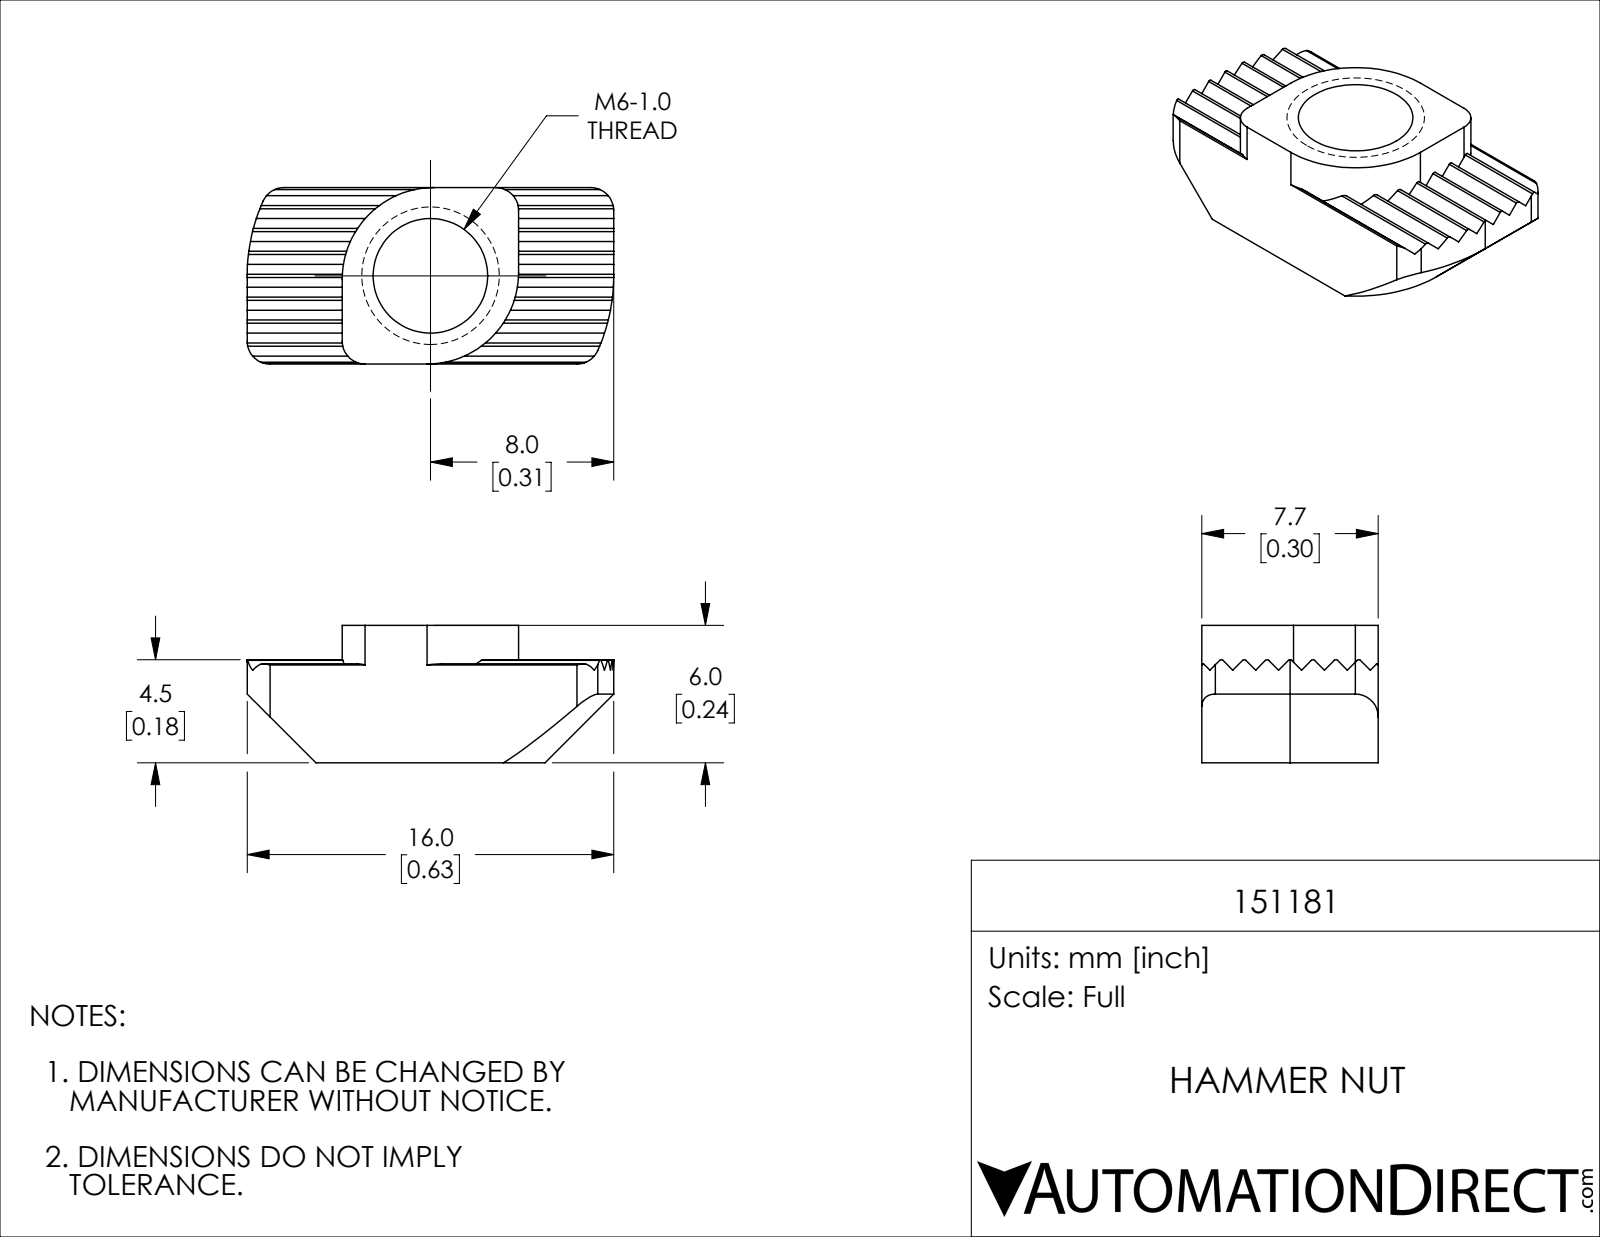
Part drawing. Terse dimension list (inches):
name: 151181
written by: SolidWorks 2021 (CONFIG_CONTROL_DESIGN)
unit: in
bodies: 1 solid, 76 faces (42 planar, 32 cylindrical, 2 other)
size: 0.63 × 0.303 × 0.236
volume: 0.025 in³; area: 0.795 in²
holes: 1× ⌀0.197
rounds: 7× R0.004, 6× R0.039, 2× R0.157, 1× R0.315
face distances: 0.303, 0.028, 0.083, 0.056, 0.236, 0.111, 0.139, 0.028, 0.167, 0.056
